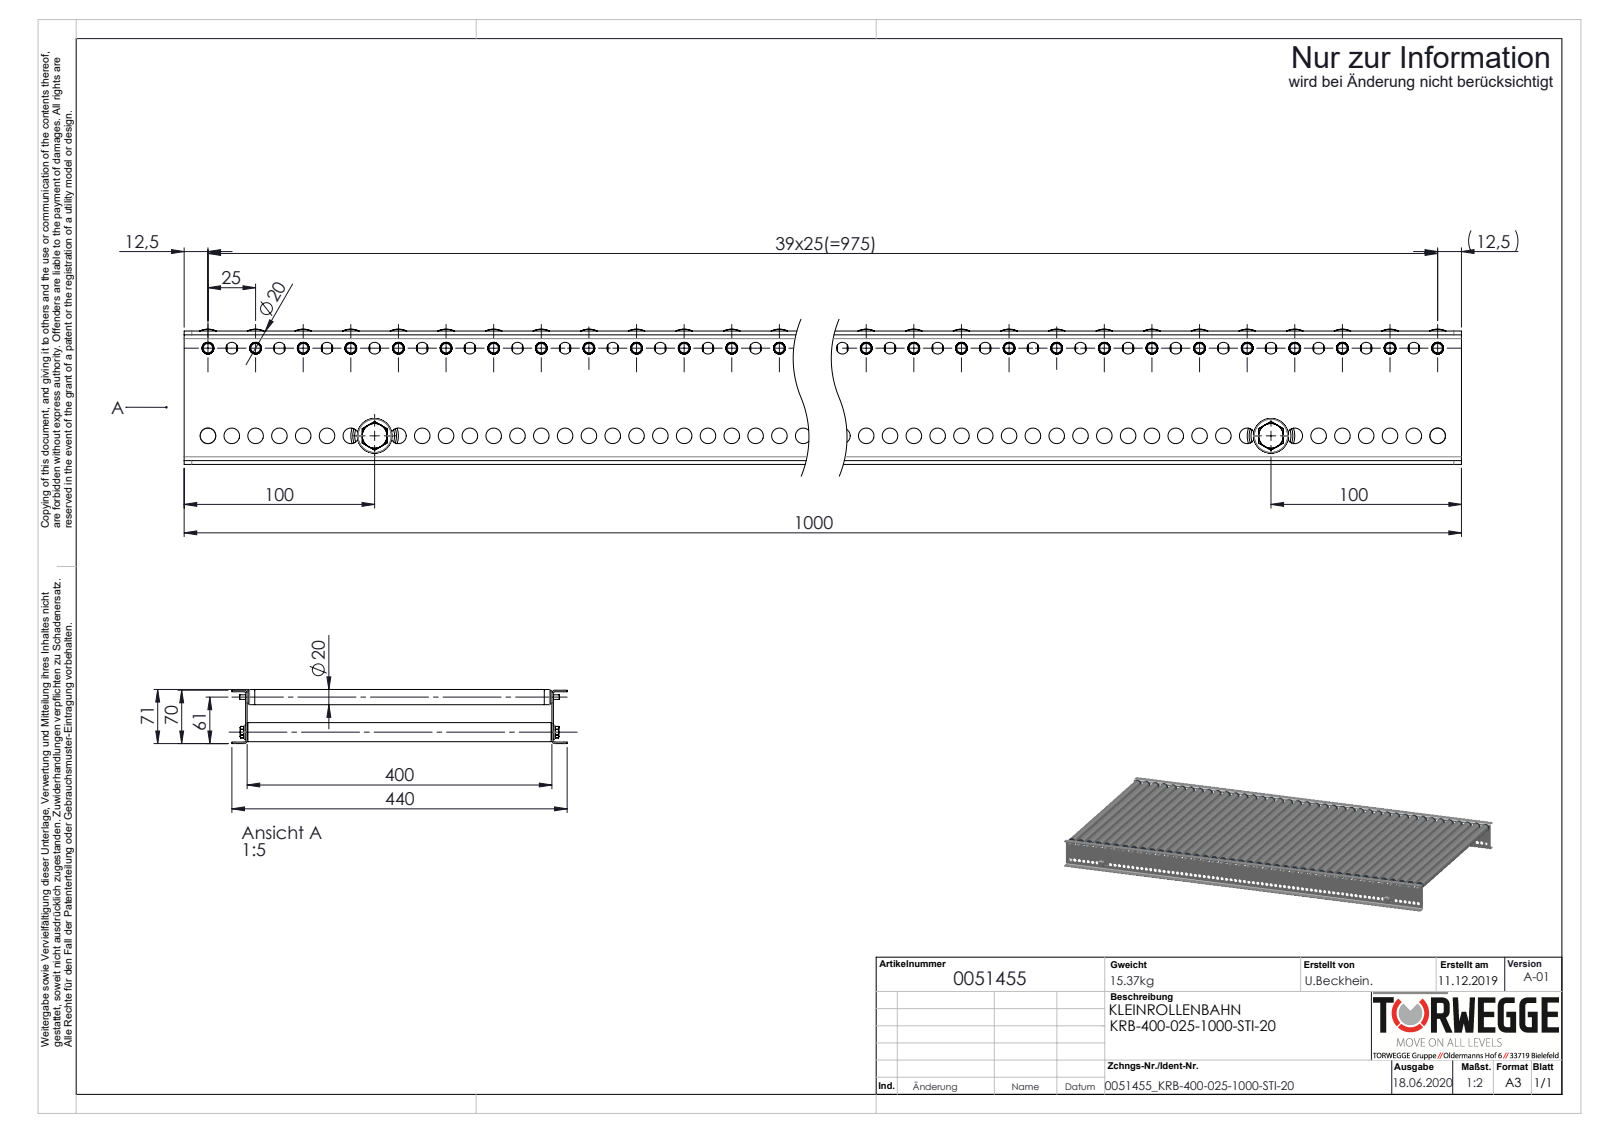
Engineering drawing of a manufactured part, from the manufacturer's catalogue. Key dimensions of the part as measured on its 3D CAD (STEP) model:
Part name (STEP PRODUCT): S100994_Sperrzahnschraube_M08x16-8.8-A2K; S100993_Tragrollenrohr-Ø20x1STI_KFG_L=380; KUT50-20x1,5-STI-A6_FA-EL=KFG_S100910_KUT50-20x1-STI-A6-FA-EL=400; 0039777_Achse-Ø06-FA-KFG_L=420 fr D20 (+4 more)
STEP written by: SolidWorks 2020 (AUTOMOTIVE_DESIGN)
Units: millimetres
Bodies: 92 solids, 7952 faces (2600 planar, 3008 cylindrical, 2344 other)
Overall size (bounding box): 1000 × 440 × 71
Volume: 1 913 000 mm³ · Surface area: 2 932 000 mm²
Round holes (diameter × count): ⌀6.2 ×79, ⌀8.2 ×79, ⌀6.1 ×40, ⌀14.2 ×40, ⌀17.2 ×40, ⌀18 ×40, ⌀6.8 ×2, ⌀21 ×2
Round bosses / shafts (diameter × count): ⌀20 ×40, ⌀19.9 ×40, ⌀18.1 ×40, ⌀17.8 ×40, ⌀16.5 ×40, ⌀6 ×40, ⌀25 ×2, ⌀8 ×2
Partial cylindrical surfaces — rounded edges, fillets, slot ends (radius × count): R4.05 ×40, R4 ×8, R2 ×4
Main face-to-face distances: 2, 402, 68, 400, 404, 66, 70, 392, 18, 30
Hole centre spacings: 12.5, 25, 37.5, 50, 62.5, 75, 87.5, 100
